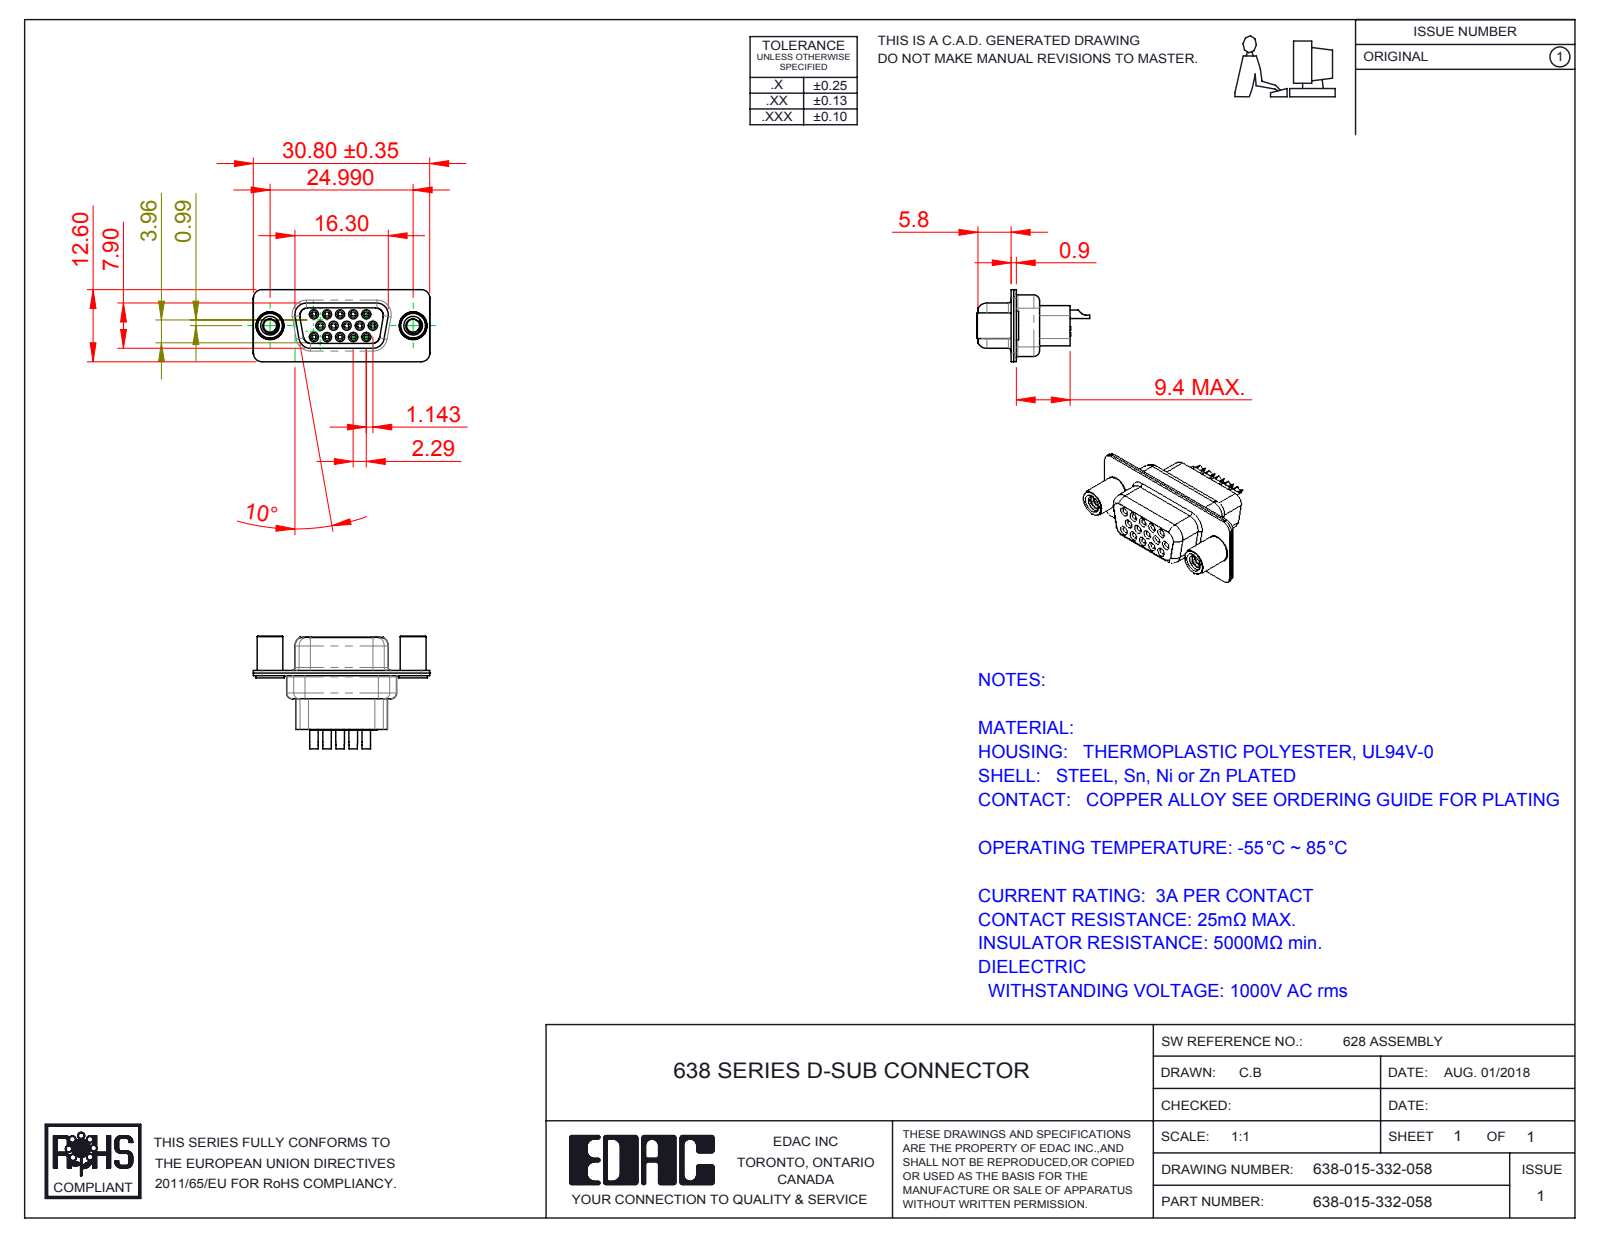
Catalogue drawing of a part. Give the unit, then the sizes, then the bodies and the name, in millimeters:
Units: millimetres
Overall size (bounding box): 30.81 × 19.7 × 12.6
Round holes (diameter × count): ⌀0.8 ×15, ⌀1 ×15, ⌀1.1 ×15, ⌀1.6 ×15, ⌀1.7 ×15, ⌀1.8 ×15, ⌀2 ×2, ⌀2.26 ×2, ⌀4 ×2, ⌀4.05 ×2, ⌀4.85 ×2
Round bosses / shafts (diameter × count): ⌀2 ×15, ⌀1.5 ×15, ⌀1.2 ×15, ⌀5 ×2, ⌀4.95 ×2, ⌀4.8 ×2, ⌀4.5 ×2
Partial cylindrical surfaces — rounded edges, fillets, slot ends (radius × count): R1.5 ×20, R2 ×12, R0.28 ×10, R1.55 ×8, R1 ×7, R1.35 ×5, R0.25 ×4, R0.5 ×4
Main face-to-face distances: 0.45, 0.9, 0.4, 1.43, 8.88, 6.6, 7, 0.85, 2.28, 9.4
Hole centre spacings: 3.96, 2.28, 4.57, 2.29, 6.05, 6.04, 6.86, 7.92
Volume: 1 928 mm³ · Surface area: 6 508 mm²
Bodies: 20 solids, 1648 faces (384 planar, 540 cylindrical, 724 other)
Part name (STEP PRODUCT): 638-015-332-058; 638 Housing_15 Contacts HP; 638 Shell Rear_15 Contacts; 638 Contact Row 3_32H (+4 more)
STEP written by: SolidWorks 2016 (CONFIG_CONTROL_DESIGN)
